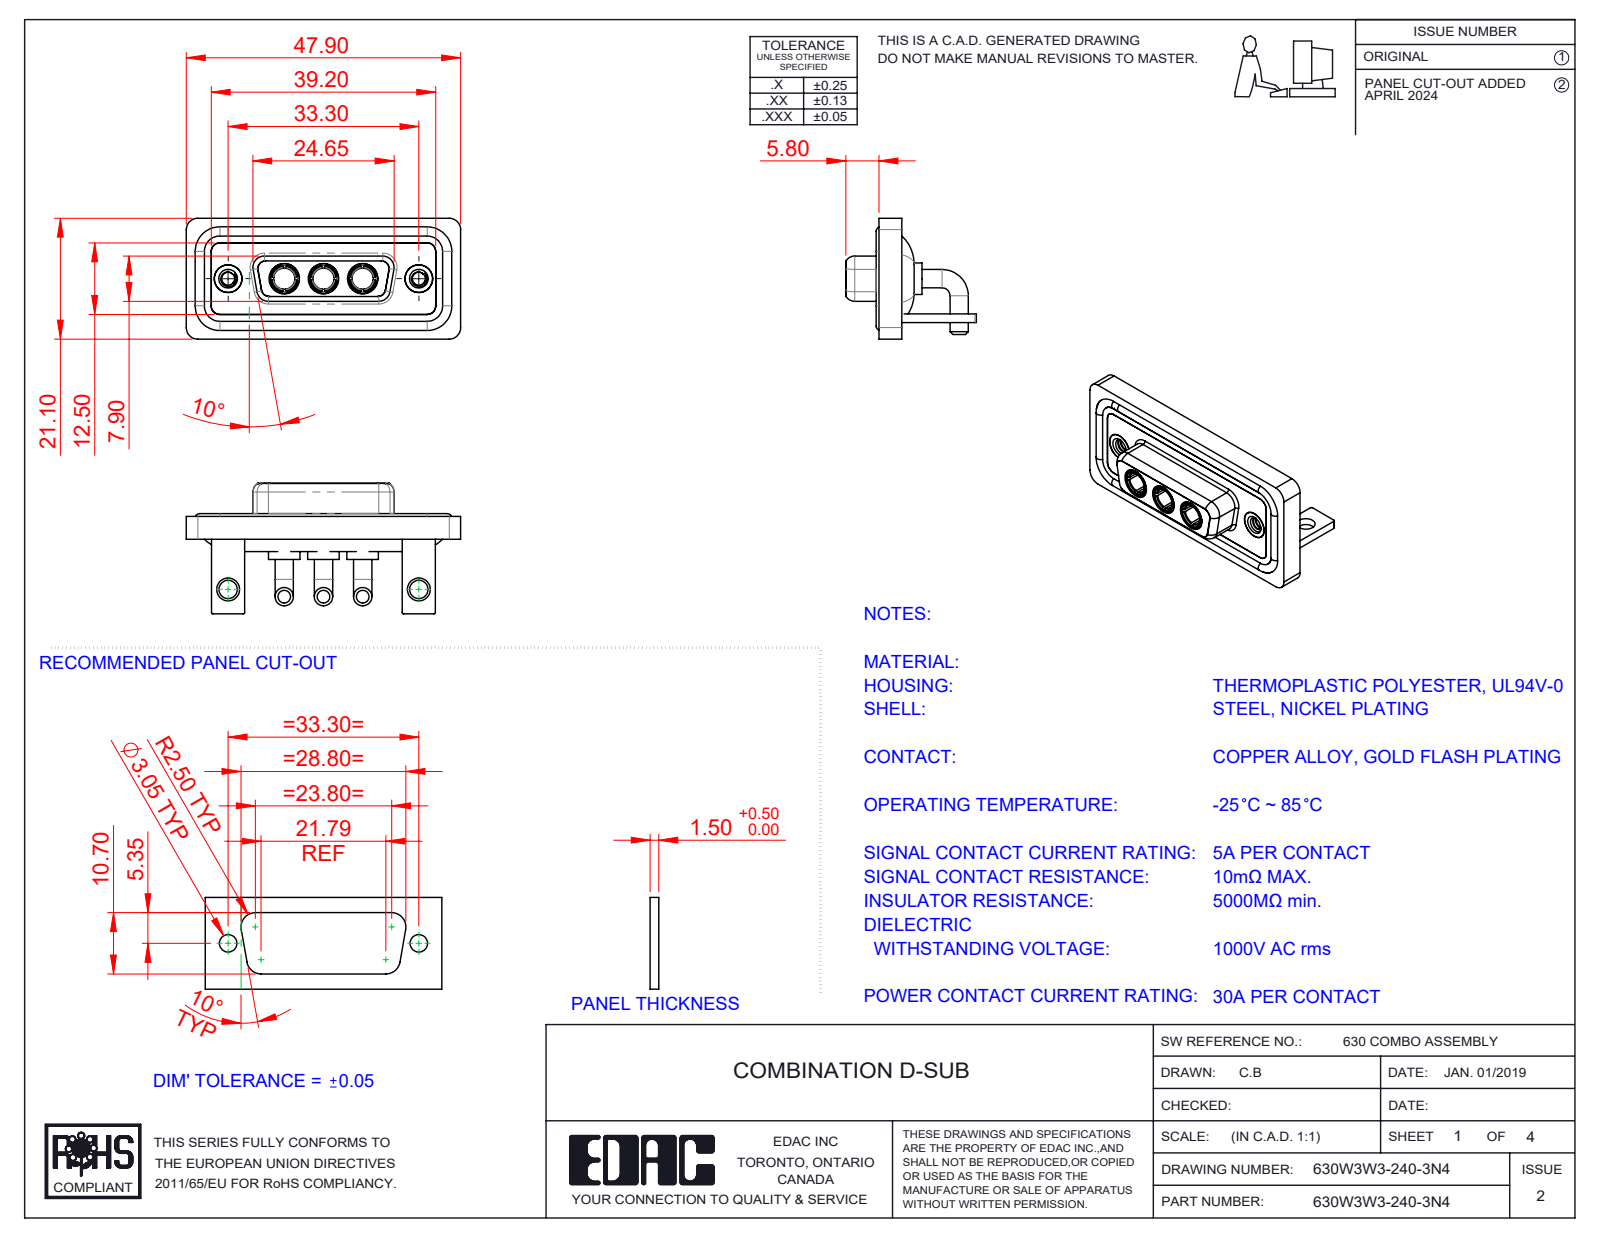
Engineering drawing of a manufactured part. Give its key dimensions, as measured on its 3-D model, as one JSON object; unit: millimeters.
{"part_name": "630Combo Shell Rear_15 Contacts; 630Combo Housing_3W3; 630Combo Threaded Rivet_2; 630Combo Waterproof Housing_15 Contacts (+4 more)", "step_written_by": "SolidWorks 2023 (CONFIG_CONTROL_DESIGN)", "units": "millimeters", "bodies": {"solids": 15, "faces": 668, "planar": 212, "cylindrical": 287, "other": 169}, "overall_size": [47.9, 22.8, 21.1], "volume_mm3": 6630, "surface_area_mm2": 10762, "round_holes": [[4.85, 5], [3.7, 3], [5.3, 3], [2.26, 2], [3.2, 2], [4, 2], [4.05, 2], [5, 2]], "round_bosses_or_shafts": [[3.2, 6], [1.6, 4], [5.5, 3], [5.2, 3], [4.96, 3], [4.75, 3], [3.75, 3], [4.95, 2]], "partial_cylinders_radius": [[2, 21], [1.5, 18], [0.25, 16], [1.35, 12], [1.6, 8], [0.5, 5], [0.6, 4], [0.65, 4]], "face_to_face_distances": [0.4, 2.9, 1.5, 1.8, 3.7, 1.1, 4.1, 1.6, 2.5, 1.4], "hole_center_spacings": [6.85, 9.8, 16.65, 23.5, 33.3, 13.7]}
